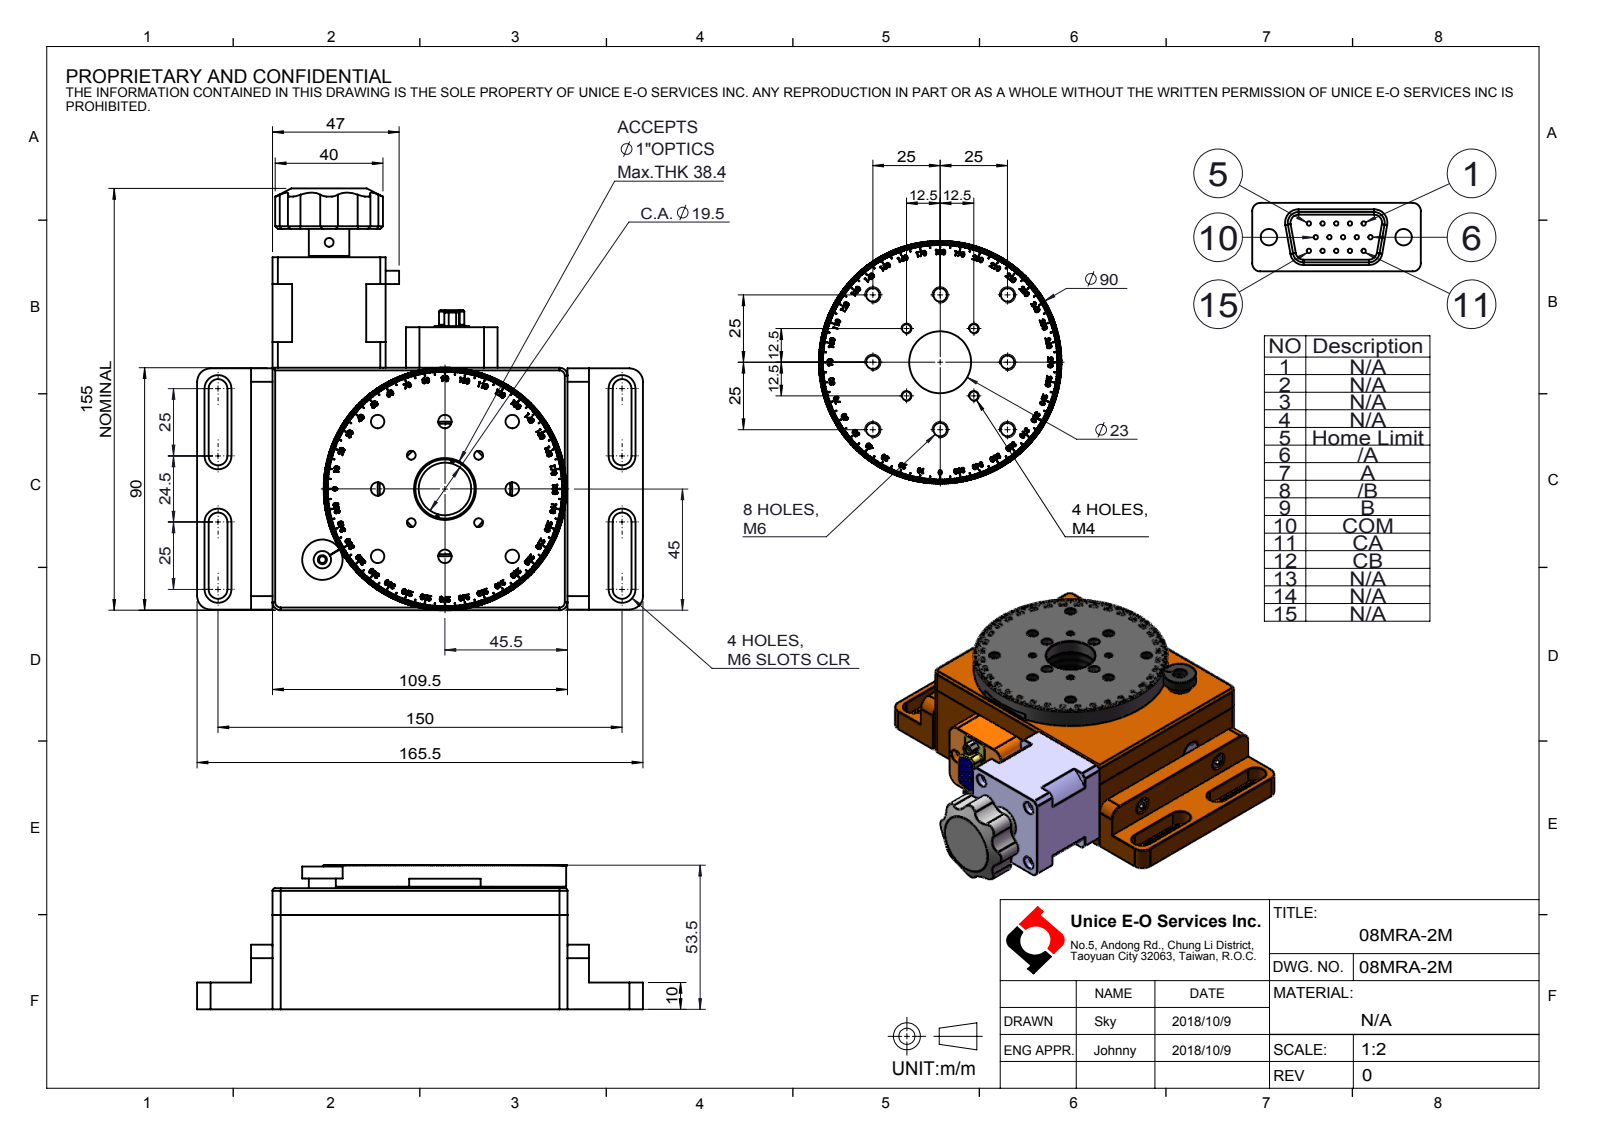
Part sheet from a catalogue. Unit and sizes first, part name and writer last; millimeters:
Units: millimetres
Overall size (bounding box): 165.5 × 156.5 × 53.5
Round holes (diameter × count): ⌀0.8 ×15, ⌀5 ×12, ⌀6.5 ×7, ⌀3.3 ×6, ⌀2.9 ×4, ⌀5.5 ×4, ⌀6.1 ×4, ⌀2.5 ×3, ⌀3.4 ×3, ⌀1.5 ×2, ⌀8 ×2, ⌀1 ×1
Round bosses / shafts (diameter × count): ⌀15 ×2, ⌀7 ×2, ⌀90 ×1, ⌀49 ×1, ⌀10 ×1
Partial cylindrical surfaces — rounded edges, fillets, slot ends (radius × count): R5 ×18, R0.5 ×8, R3.5 ×8, R4 ×8, R7.41 ×8, R1 ×4, R1.5 ×4, R2 ×4
Main face-to-face distances: 45, 8, 0.5, 8.5, 109.5, 53.5, 45.5, 90, 42, 10
Hole centre spacings: 17.68, 2.84, 25, 39.53, 4.58, 5.08, 2.54, 6.84
Bodies: 0 solids, 1138 faces (792 planar, 250 cylindrical, 96 other)
Part name (STEP PRODUCT): 08MRA-2M
STEP written by: SolidWorks 2016 (AUTOMOTIVE_DESIGN)
